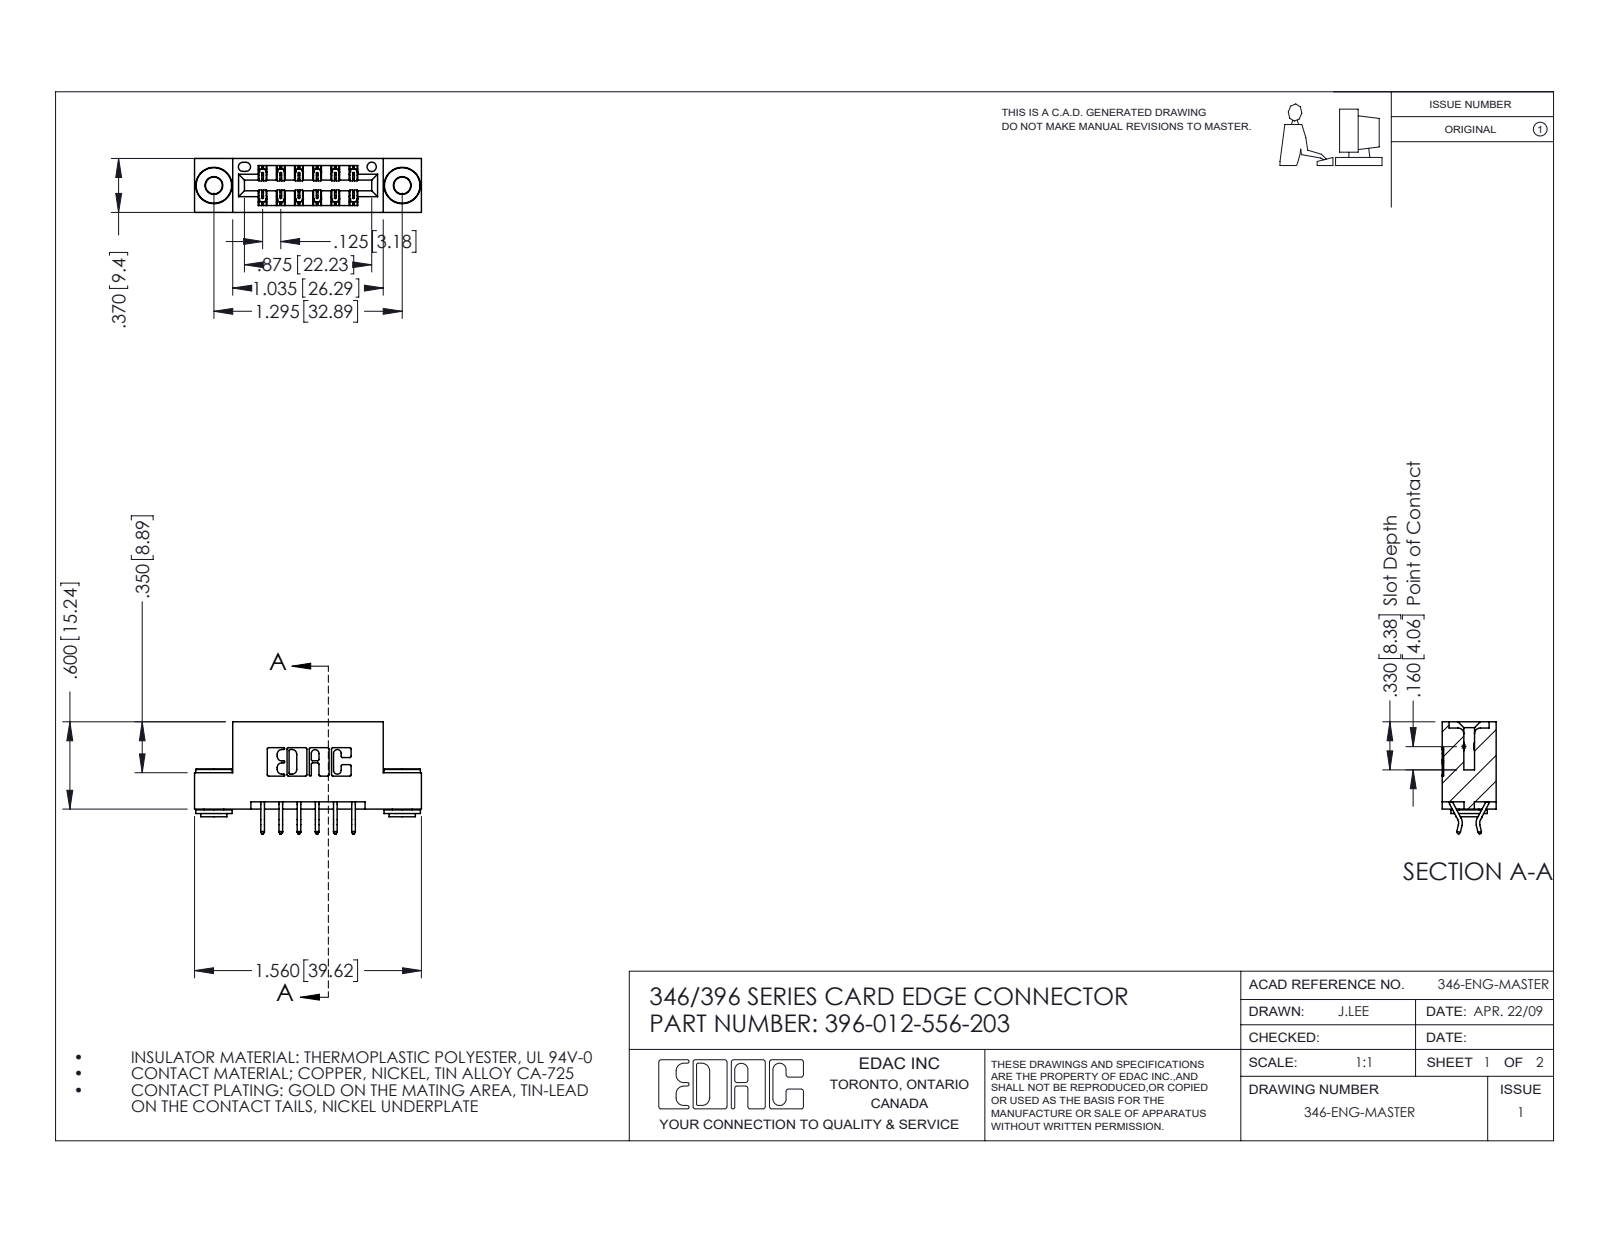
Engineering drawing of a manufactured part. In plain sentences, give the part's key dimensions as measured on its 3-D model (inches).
The part is named "346 Part_Flush Mounting Lugs - 0.156 Dia-TH; 345-250-002_345-250-002-102; 345-292-001_556 Tail; 396-012-556-203". Its 3-D file was written by "SolidWorks 2016 (CONFIG_CONTROL_DESIGN)". It is 15 solids with 856 faces: 554 planar, 294 cylindrical and 8 other. Overall it measures 1.56 by 0.77 by 0.37 inches. Its volume is 0.22 cubic inches and its surface area 7.114 square inches. Round holes: 2 of diameter 0.116, 2 of diameter 0.156, 1 of diameter 0.064. Round bosses or shafts: 2 of diameter 0.25, 2 of diameter 0.18, 2 of diameter 0.136. Partial cylindrical surfaces (rounded edges, fillets, slot ends): 22 of radius 0.01, 18 of radius 0.006, 6 of radius 0.007, 6 of radius 0.031, 3 of radius 0.026, 2 of radius 0.01, 2 of radius 0.014, 2 of radius 0.022. The main face-to-face distances are 0.25, 0.37, 0.048, 0.322, 0.025, 0.148, 0.222, 0.1, 0.174, 0.072. The hole center spacings are 0.246, 1.092, 1.295.
